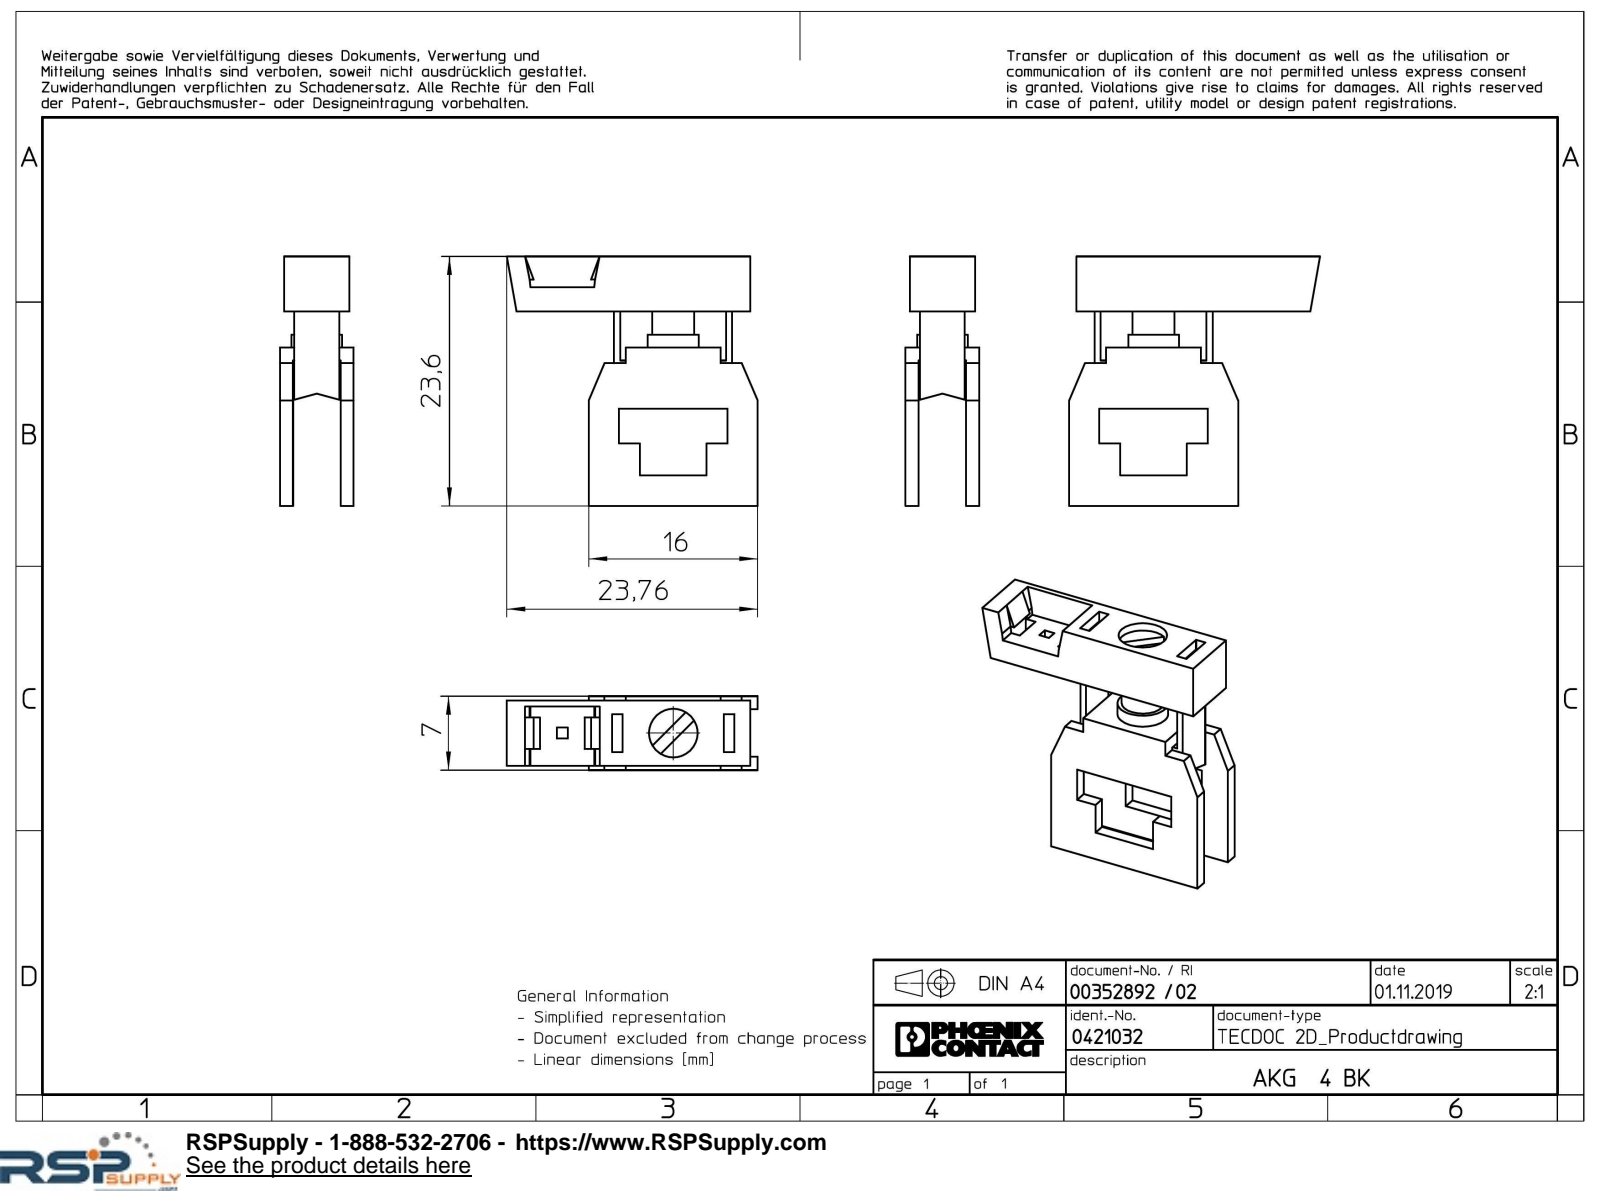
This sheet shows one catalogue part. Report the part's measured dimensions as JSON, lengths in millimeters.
{"part_name": "AKG_4_BK-select", "step_written_by": "Creo Elements/Direct Modeling 20.1A 29-Sep-2018 (C) Parametric Technology GmbH (AUTOMOTIVE_DESIGN)", "units": "millimeters", "bodies": {"solids": 1, "faces": 107, "planar": 101, "cylindrical": 6, "other": 0}, "overall_size": [23.76, 23.6, 7], "volume_mm3": 1296, "surface_area_mm2": 1910, "round_holes": [[4.6, 1]], "round_bosses_or_shafts": [[4.8, 1], [4, 1]], "face_to_face_distances": [1.25, 5.75, 6.6, 0.4, 0.85, 5.35, 7, 4.5, 0.98, 6.2]}
